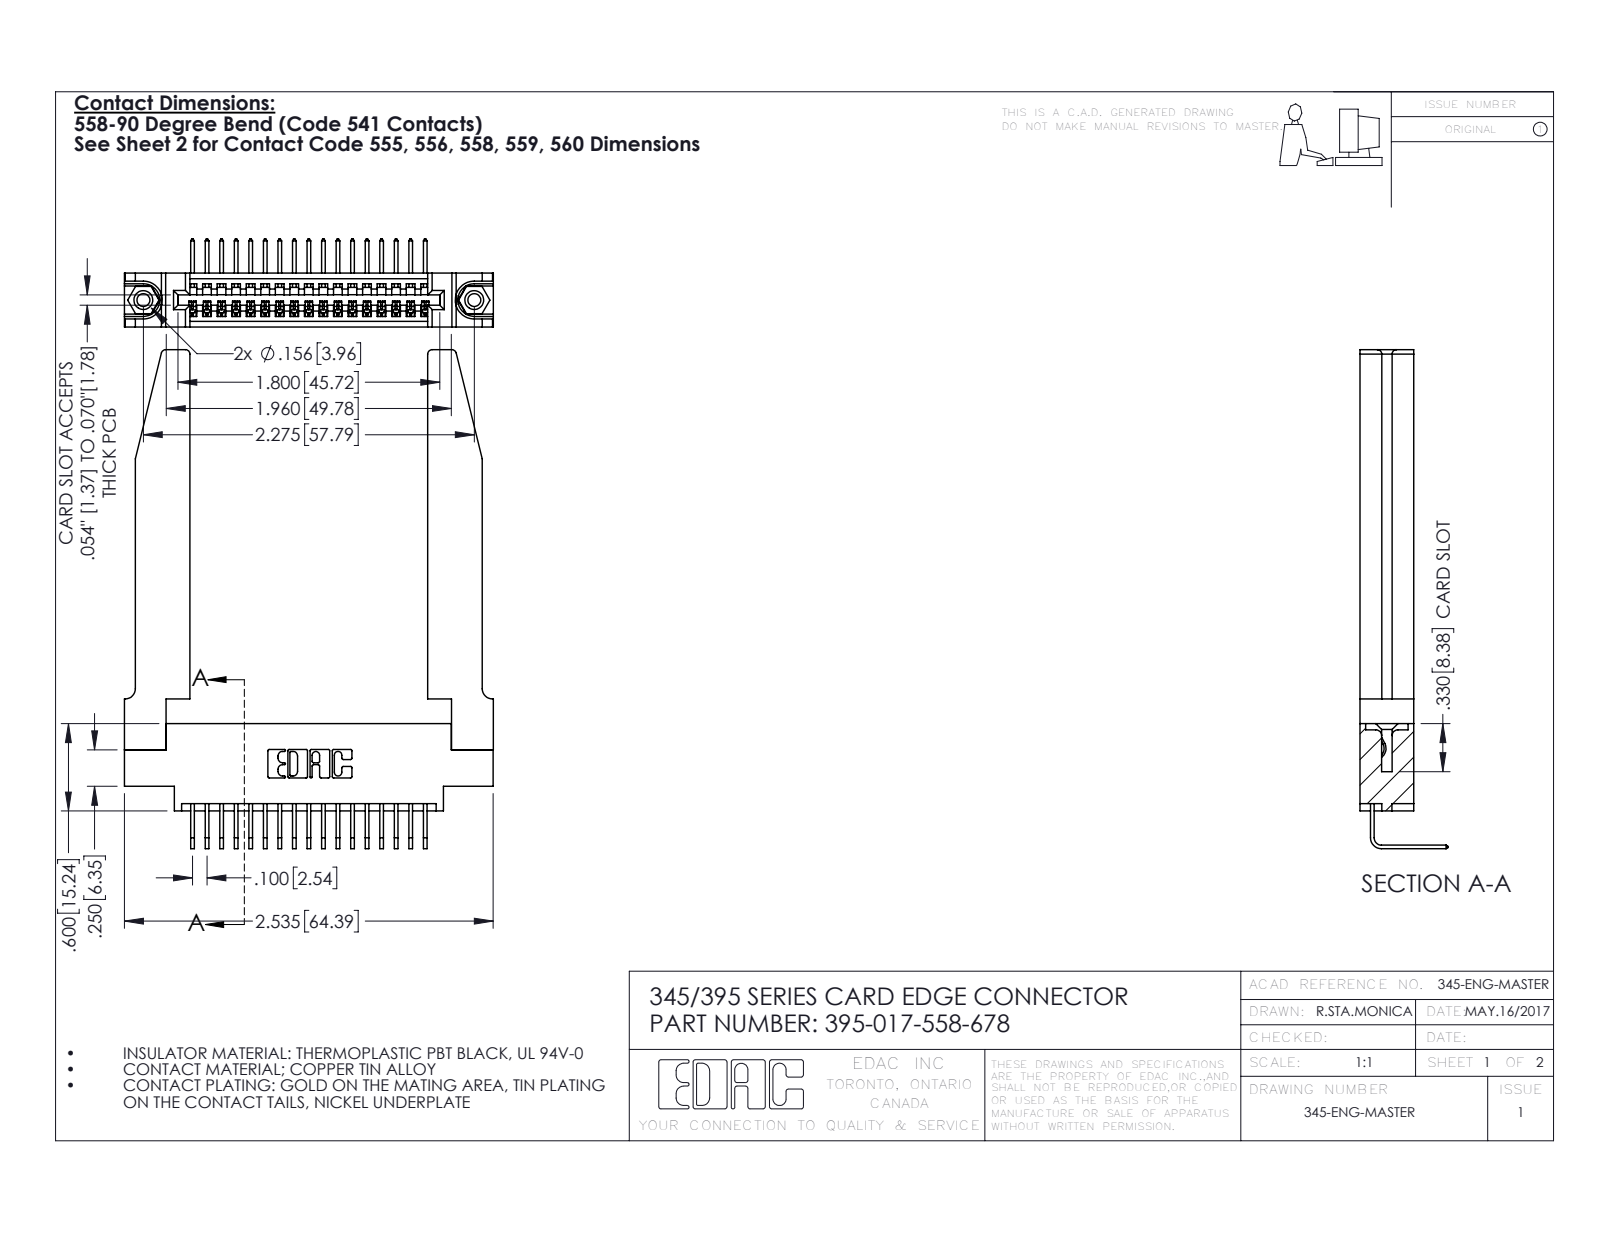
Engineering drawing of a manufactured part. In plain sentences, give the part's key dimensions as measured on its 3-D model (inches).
The part is named "345-220-078_345-220-078; 395-017-558-678; 345-250-001_345-250-001-102; 345 Part_0.170 Offset - 0.156 Dia-TH (+1 more)". Its 3-D file was written by "SolidWorks 2016 (CONFIG_CONTROL_DESIGN)". It is 22 solids with 1384 faces: 940 planar, 392 cylindrical and 52 other. Overall it measures 3.429 by 2.536 by 0.605 inches. Its volume is 0.832 cubic inches and its surface area 22.86 square inches. Round holes: 2 of diameter 0.089, 2 of diameter 0.125, 2 of diameter 0.156, 1 of diameter 0.064. Round bosses or shafts: 2 of diameter 0.155. Partial cylindrical surfaces (rounded edges, fillets, slot ends): 34 of radius 0.006, 22 of radius 0.01, 8 of radius 0.03, 6 of radius 0.007, 6 of radius 0.031, 3 of radius 0.026, 2 of radius 0.031, 2 of radius 0.04. The main face-to-face distances are 0.37, 0.072, 0.298, 0.148, 0.15, 0.098, 0.272, 0.025, 0.2, 0.22. The hole center spacings are 0.27, 2.041, 2.275.
